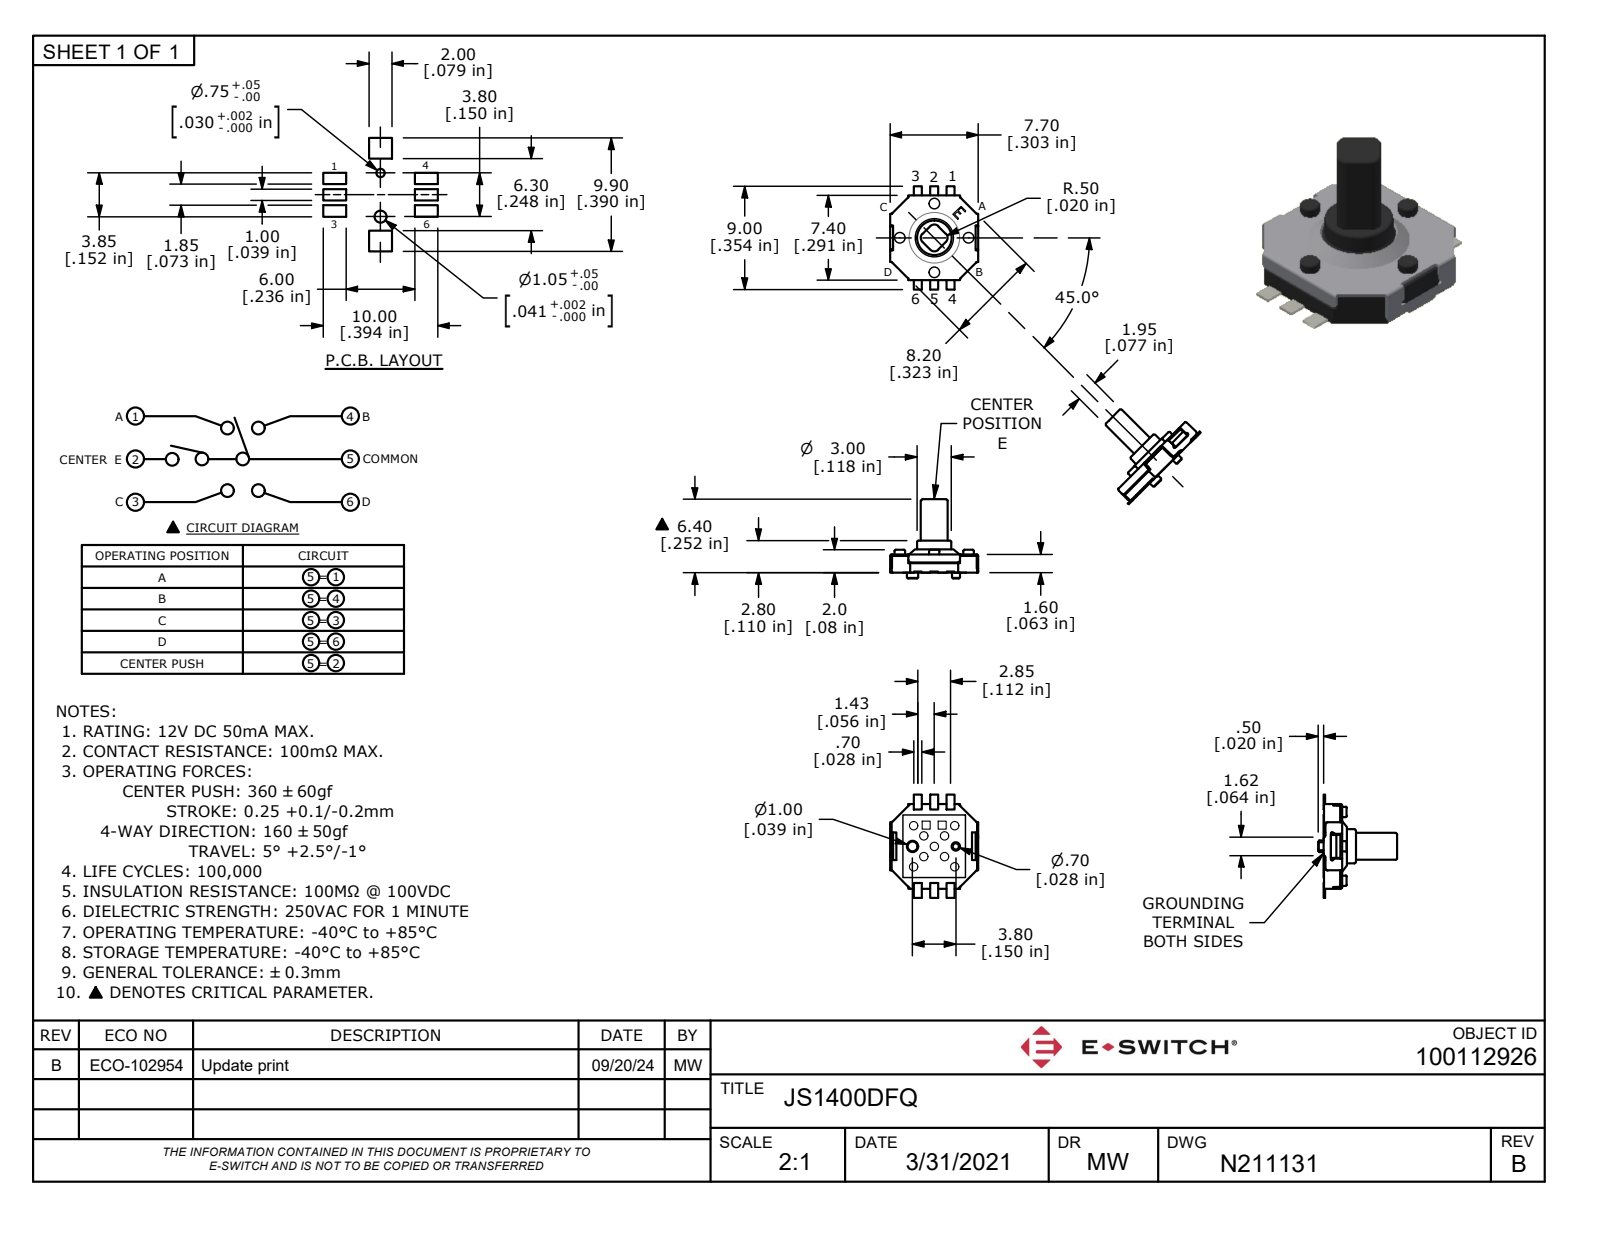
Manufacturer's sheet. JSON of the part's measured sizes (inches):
{"part_name": "100112926_Simplify_1", "step_written_by": "Autodesk Inventor 2022 (AUTOMOTIVE_DESIGN)", "units": "inches", "bodies": {"solids": 2, "faces": 284, "planar": 189, "cylindrical": 80, "other": 15}, "overall_size": [0.354, 0.303, 0.272], "volume_in3": 0.005, "surface_area_in2": 0.524, "round_holes": [[0.028, 9]], "round_bosses_or_shafts": [[0.035, 4], [0.118, 1], [0.039, 1], [0.028, 1]], "partial_cylinders_radius": [[0.008, 16], [0.004, 4], [0.005, 4], [0.006, 4], [0.02, 4], [0.049, 4]], "face_to_face_distances": [0.022, 0.014, 0.035, 0.028, 0.041, 0.063, 0.057, 0.063, 0.057, 0.021], "hole_center_spacings": [0.05, 0.112, 0.1, 0.071, 0.142, 0.15, 0.2]}
